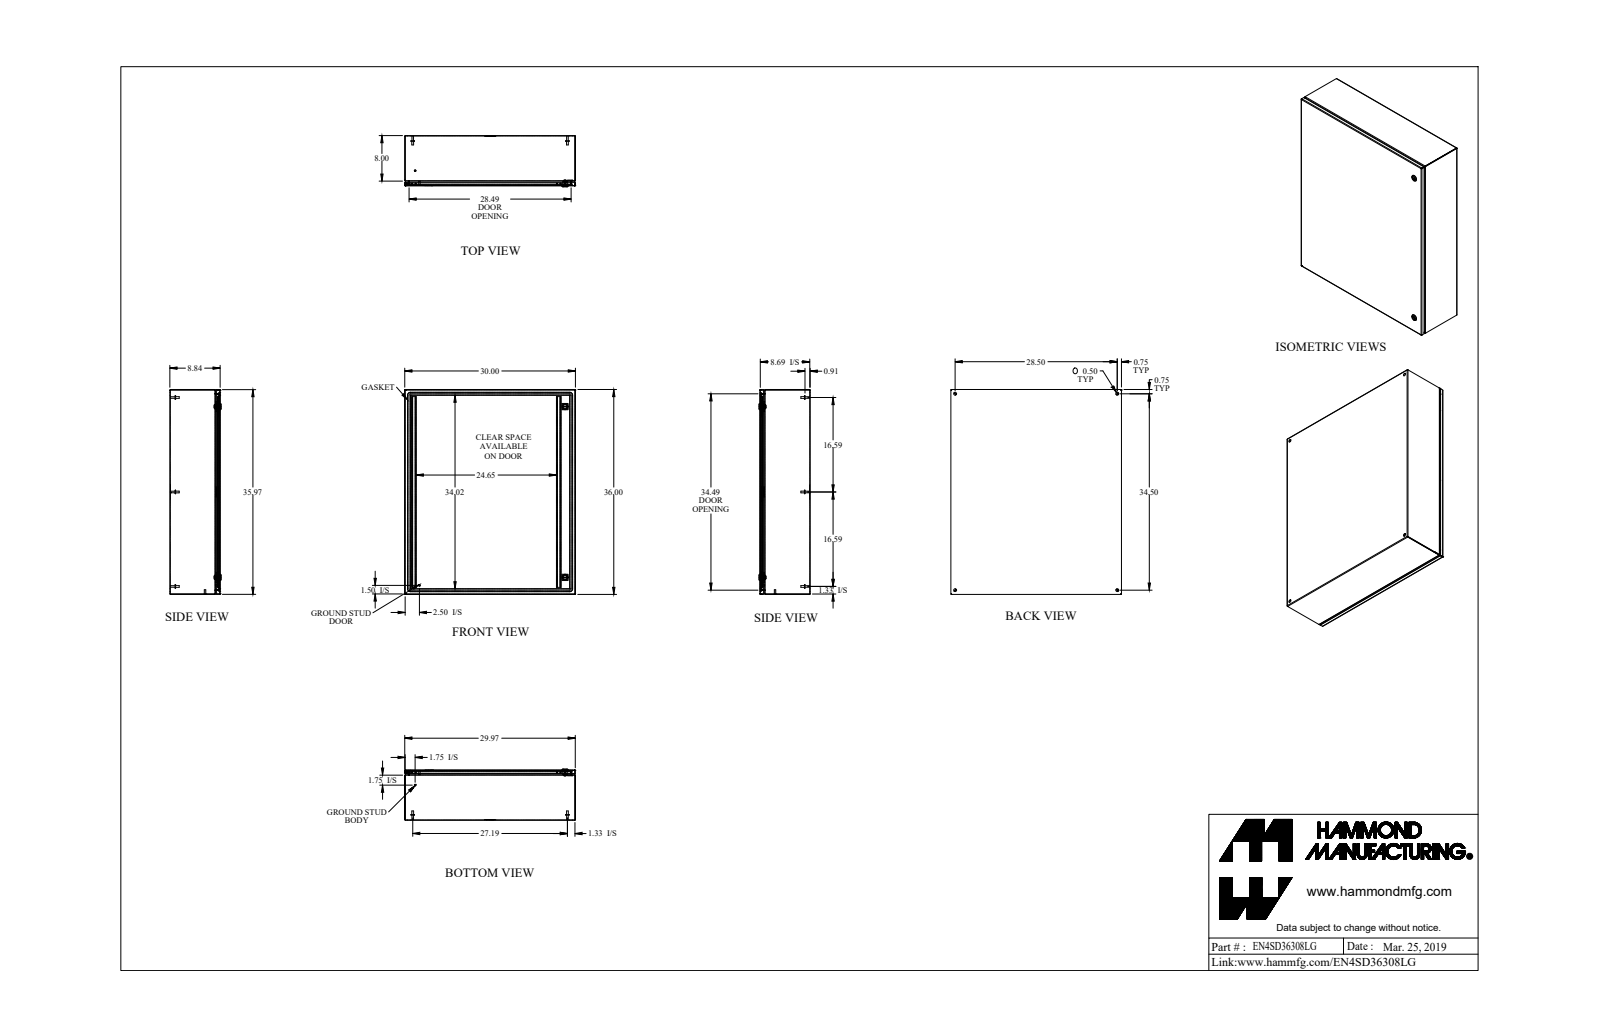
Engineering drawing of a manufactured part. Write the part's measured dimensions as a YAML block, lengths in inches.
part_name: "EN4SD36308LG_Default"
step_written_by: "SolidWorks 2019 (CONFIG_CONTROL_DESIGN)"
units: inches
bodies: {solids: 33, faces: 909, planar: 430, cylindrical: 295, other: 184}
overall_size: [36, 30, 8.997]
volume: 267.6
surface_area: 7501
round_holes:
  - {diameter: 0.5, count: 4}
  - {diameter: 0.232, count: 2}
  - {diameter: 0.625, count: 2}
  - {diameter: 0.785, count: 2}
  - {diameter: 0.172, count: 1}
  - {diameter: 0.24, count: 1}
  - {diameter: 0.242, count: 1}
round_bosses_or_shafts:
  - {diameter: 0.625, count: 6}
  - {diameter: 0.313, count: 6}
  - {diameter: 0.27, count: 6}
  - {diameter: 1.1, count: 2}
  - {diameter: 0.525, count: 2}
  - {diameter: 0.281, count: 2}
  - {diameter: 0.25, count: 2}
  - {diameter: 0.455, count: 1}
partial_cylinders:
  - {radius: 0.036, count: 20}
  - {radius: 0.108, count: 20}
  - {radius: 0.043, count: 12}
  - {radius: 0.081, count: 12}
  - {radius: 0.312, count: 10}
  - {radius: 0.006, count: 6}
  - {radius: 0.062, count: 6}
  - {radius: 0.125, count: 4}
face_to_face_distances: [0.072, 8.765, 8.693, 8.837, 29.928, 35.928, 29.856, 30, 35.856, 36]
hole_center_spacings: [27.519, 28.5, 34.5, 44.749, 2.493, 2.494, 29.999, 32.267]
